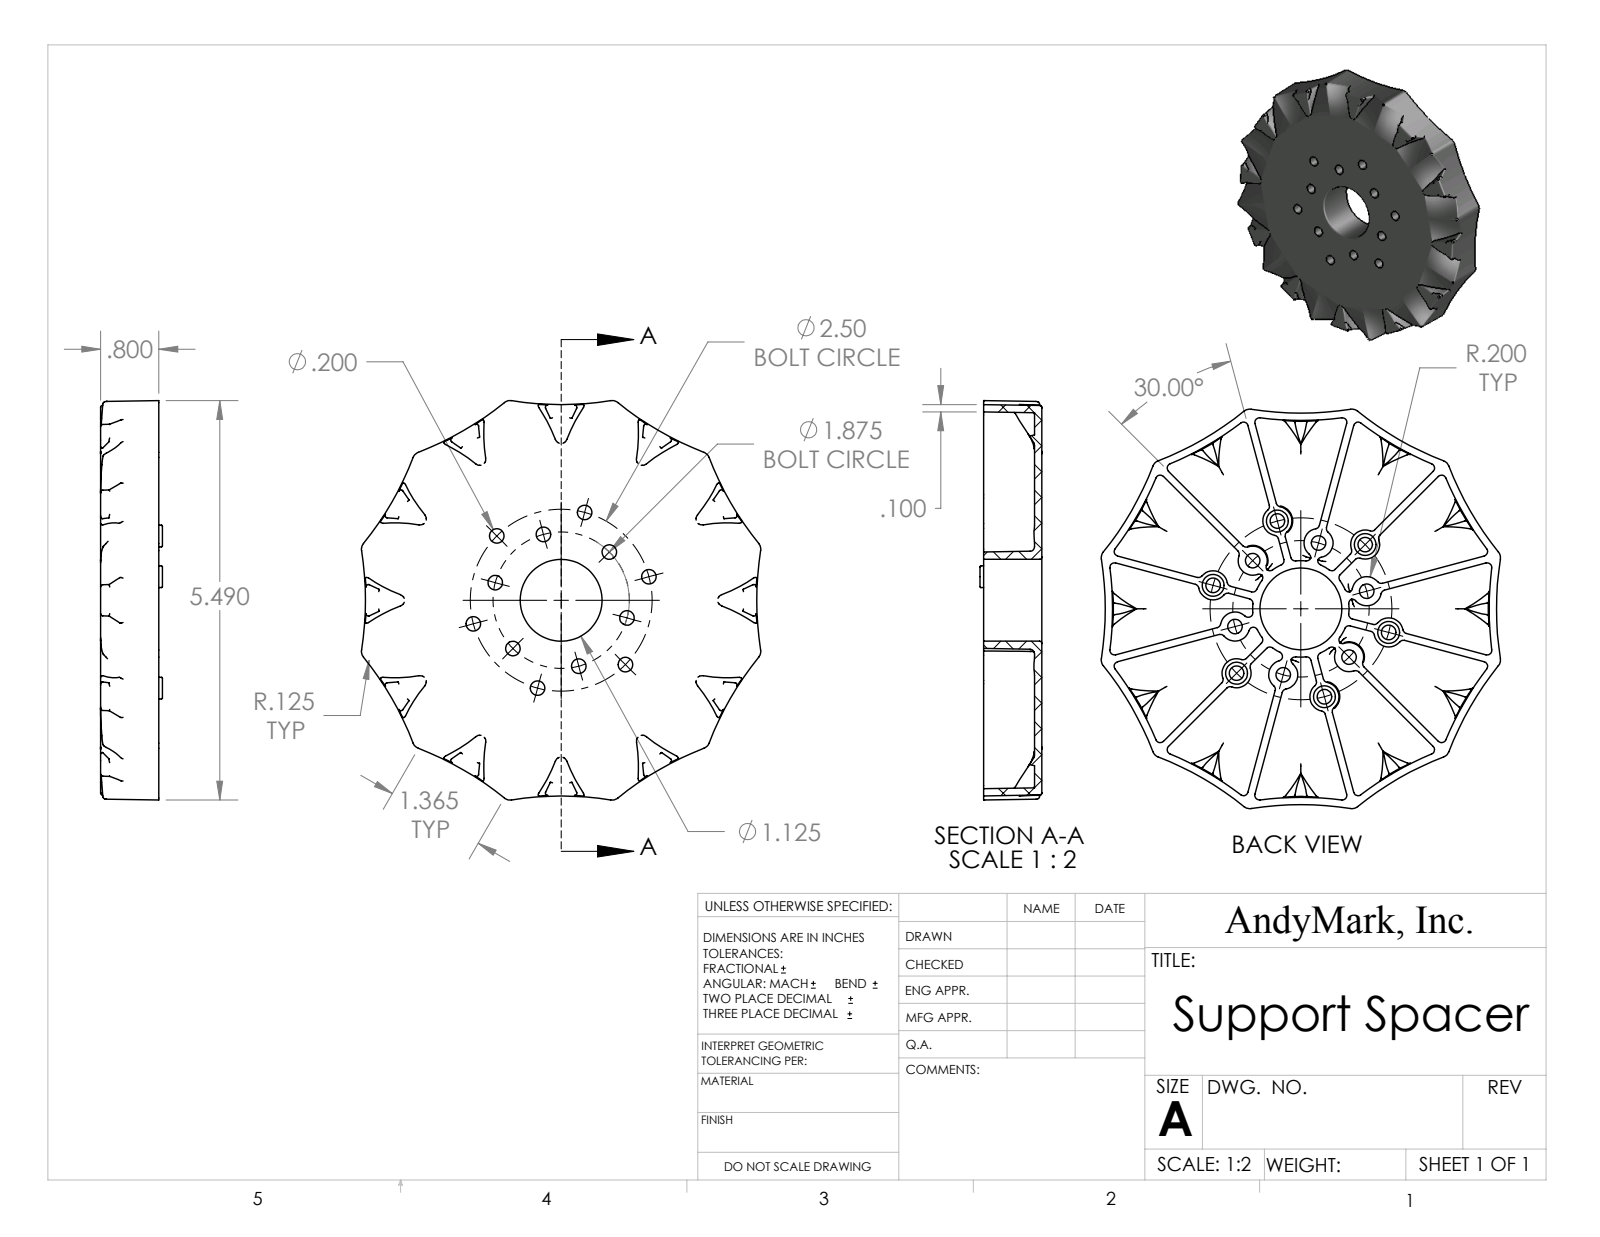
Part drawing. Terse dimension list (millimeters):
name: Support Spacer Half
written by: SolidWorks 2010 (AUTOMOTIVE_DESIGN)
unit: mm
bodies: 1 solid, 1031 faces (68 planar, 62 cylindrical, 901 other)
size: 139.4 × 139.4 × 21.6
volume: 101 300 mm³; area: 71 870 mm²
holes: 12× ⌀5.1, 1× ⌀28.6
rounds: 10× R1.6, 8× R1.6
face distances: 2.5, 20.3, 17.8, 19.1, 1.3, 16.5, 21.6
hole spacings: 16.3, 31.8, 53.7, 23.8, 39.7, 23.8, 39.7, 41.2
